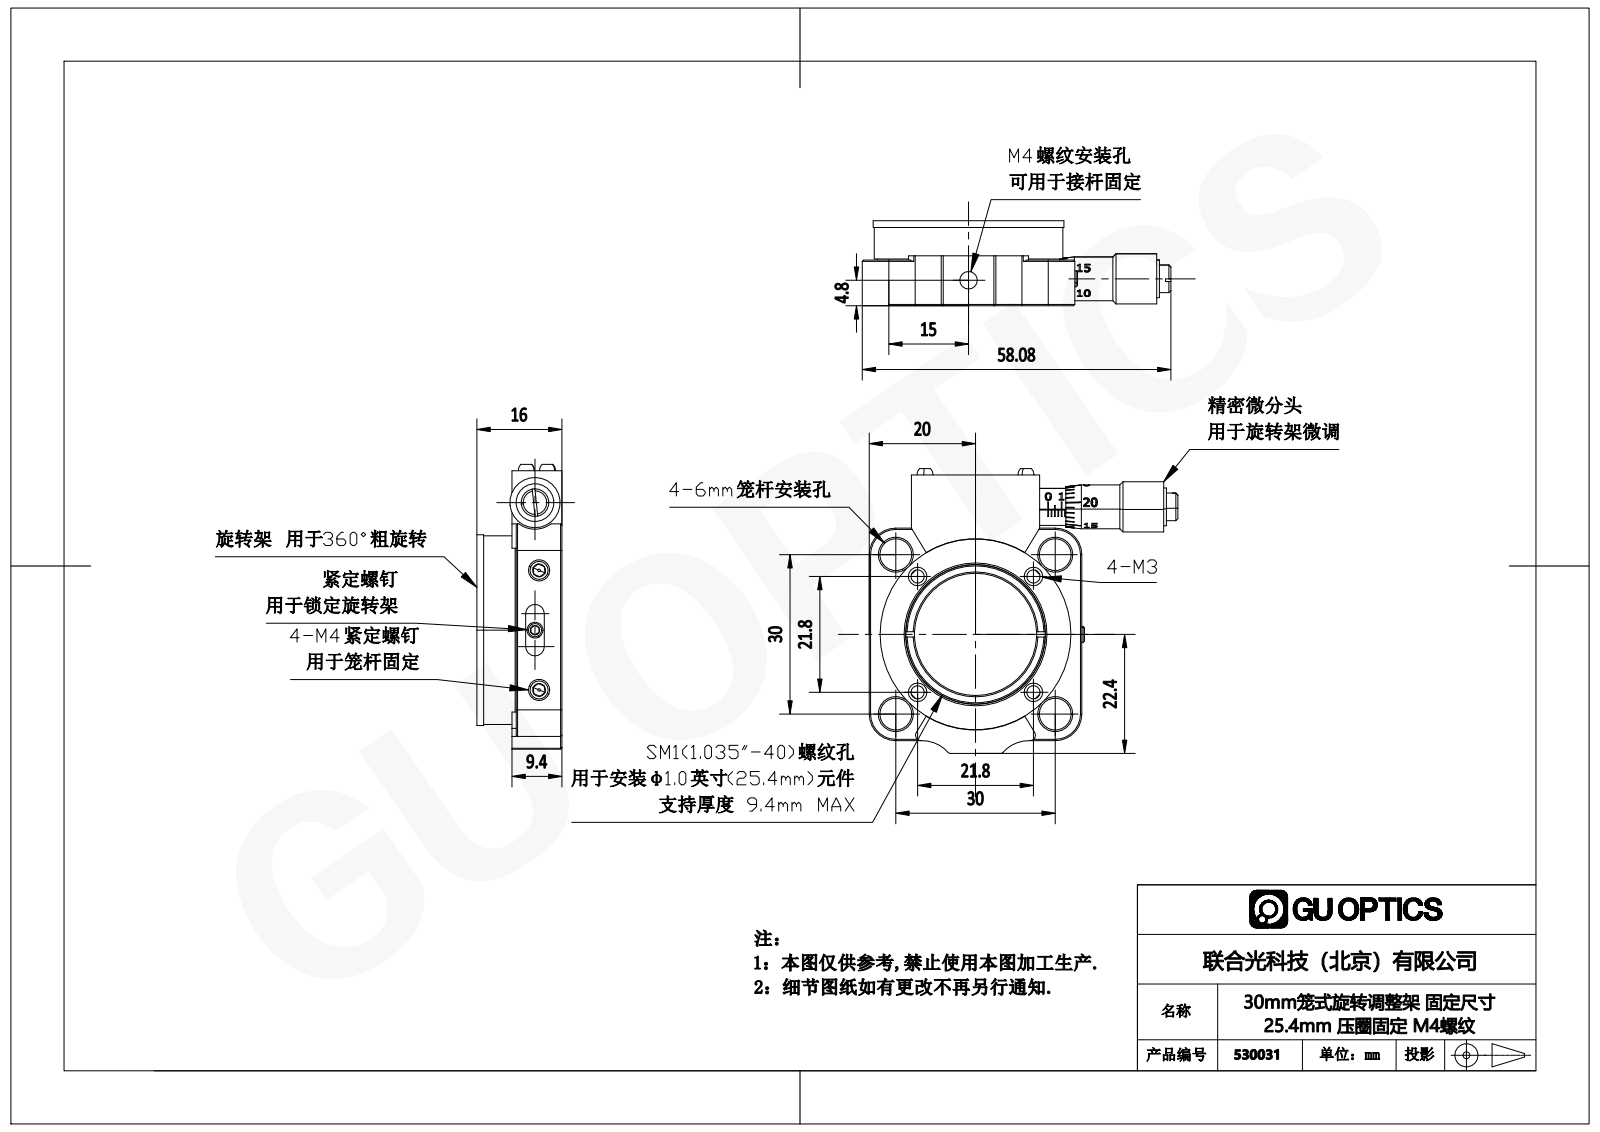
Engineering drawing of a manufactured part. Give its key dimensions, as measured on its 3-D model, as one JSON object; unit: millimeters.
{"step_written_by": "SolidWorks 2018 (AUTOMOTIVE_DESIGN)", "units": "millimeters", "bodies": {"solids": 0, "faces": 381, "planar": 132, "cylindrical": 95, "other": 154}, "overall_size": [58.08, 53.6, 16], "round_holes": [[2.5, 5], [6, 4], [4, 2], [3.3, 1], [7.24, 1], [23.01, 1], [24, 1], [26.29, 1], [34.3, 1]], "round_bosses_or_shafts": [[35.9, 1], [35.5, 1], [33.8, 1], [9.45, 1], [8.25, 1], [7.11, 1], [6.99, 1], [5.21, 1]], "partial_cylinders_radius": [[5, 5], [0.5, 2], [1, 2], [1.6, 2], [1.75, 2], [6.5, 2], [3.48, 1], [4.12, 1]], "face_to_face_distances": [16, 9.4, 6.6, 9.15, 15.75, 8.6, 8.35, 0.8, 7.4, 40], "hole_center_spacings": [26.22, 5.8, 15.41, 21.21, 21.8, 30, 36.63, 30.83]}
